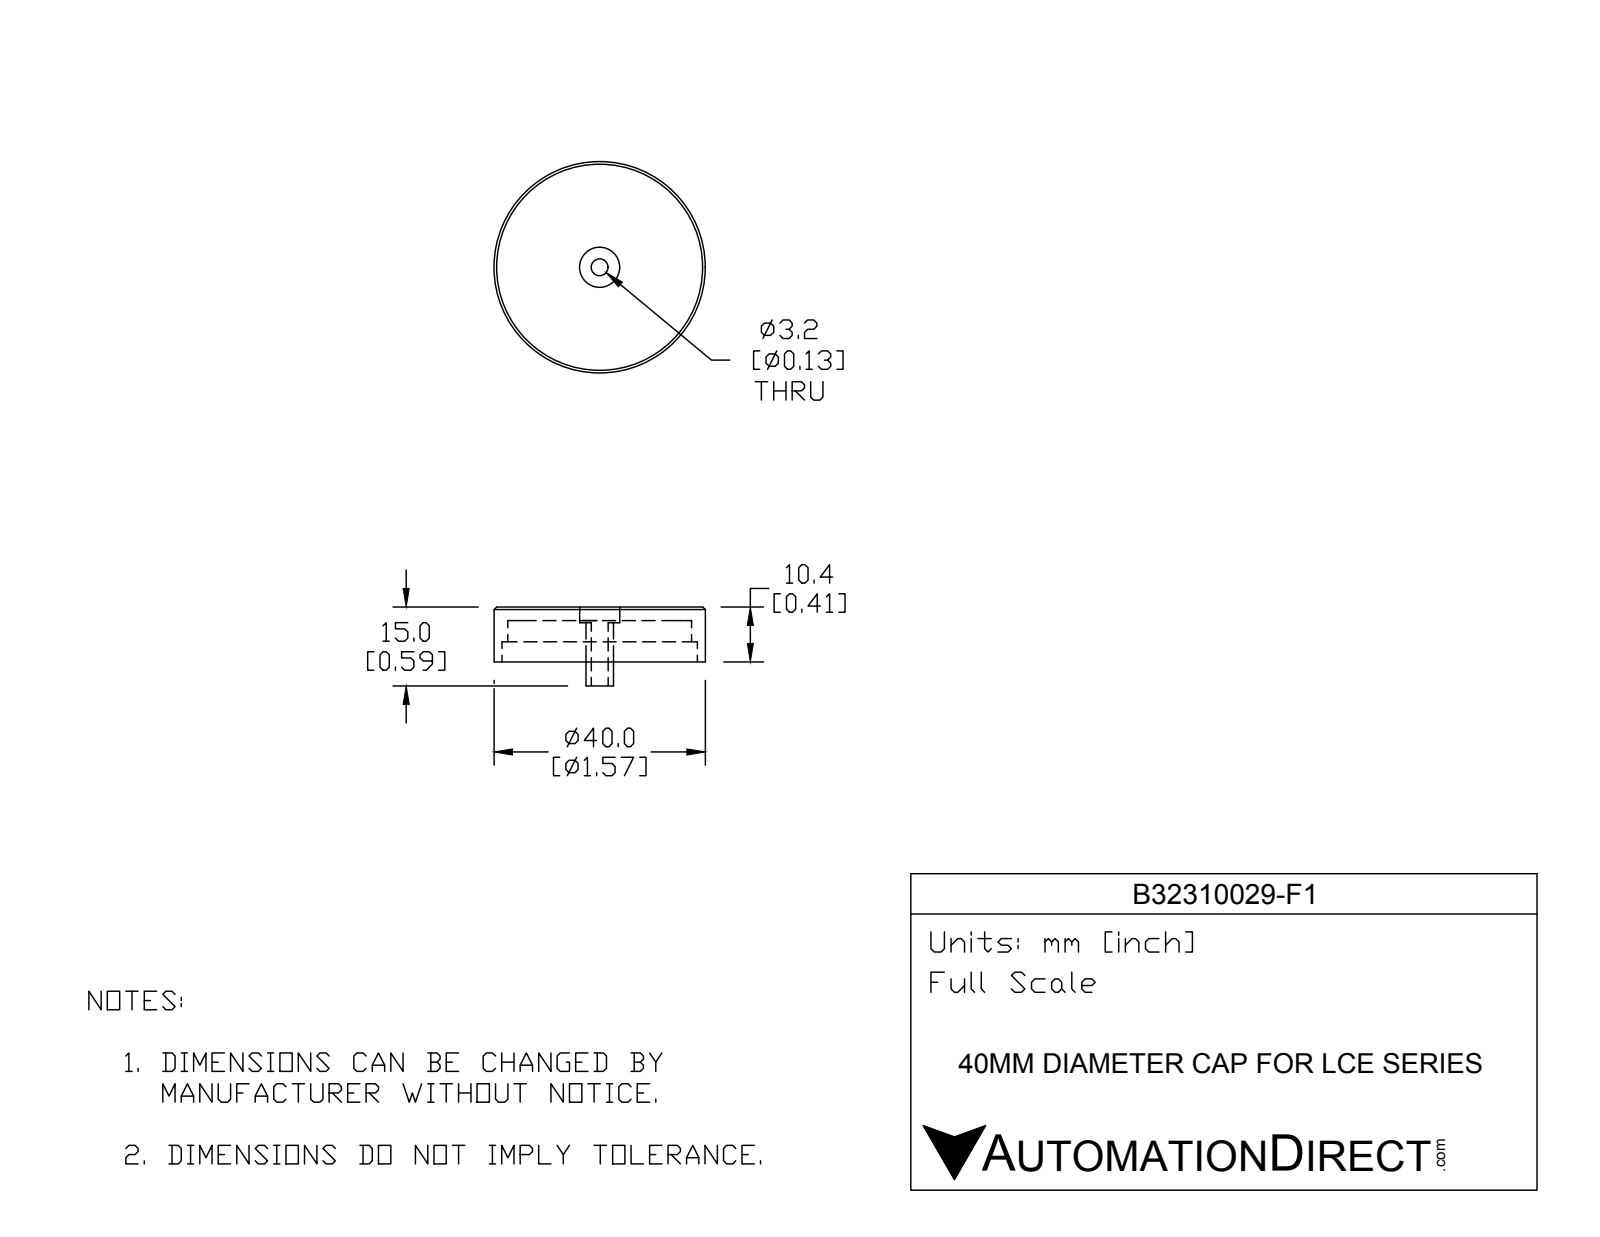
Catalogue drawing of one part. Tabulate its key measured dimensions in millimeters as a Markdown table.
| quantity | value |
| --- | --- |
| part name | B32310029-F1 |
| STEP written by | SolidWorks 2016 (AUTOMOTIVE_DESIGN) |
| units | millimeters |
| bodies | 1 solid, 44 faces (24 planar, 18 cylindrical, 2 other) |
| overall size | 40 × 40 × 14.95 |
| volume | 5 636 mm³ |
| surface area | 5 408 mm² |
| round holes (diameter × count) | 3.2 × 1, 7.6 × 1, 34.8 × 1, 37 × 1 |
| round bosses / shafts (diameter × count) | 40 × 1, 13 × 1, 5.2 × 1 |
| main face-to-face distances | 2.59, 7.81, 10.4, 5.25, 2.56, 5.15, 1, 3.81, 1.44, 4 |
